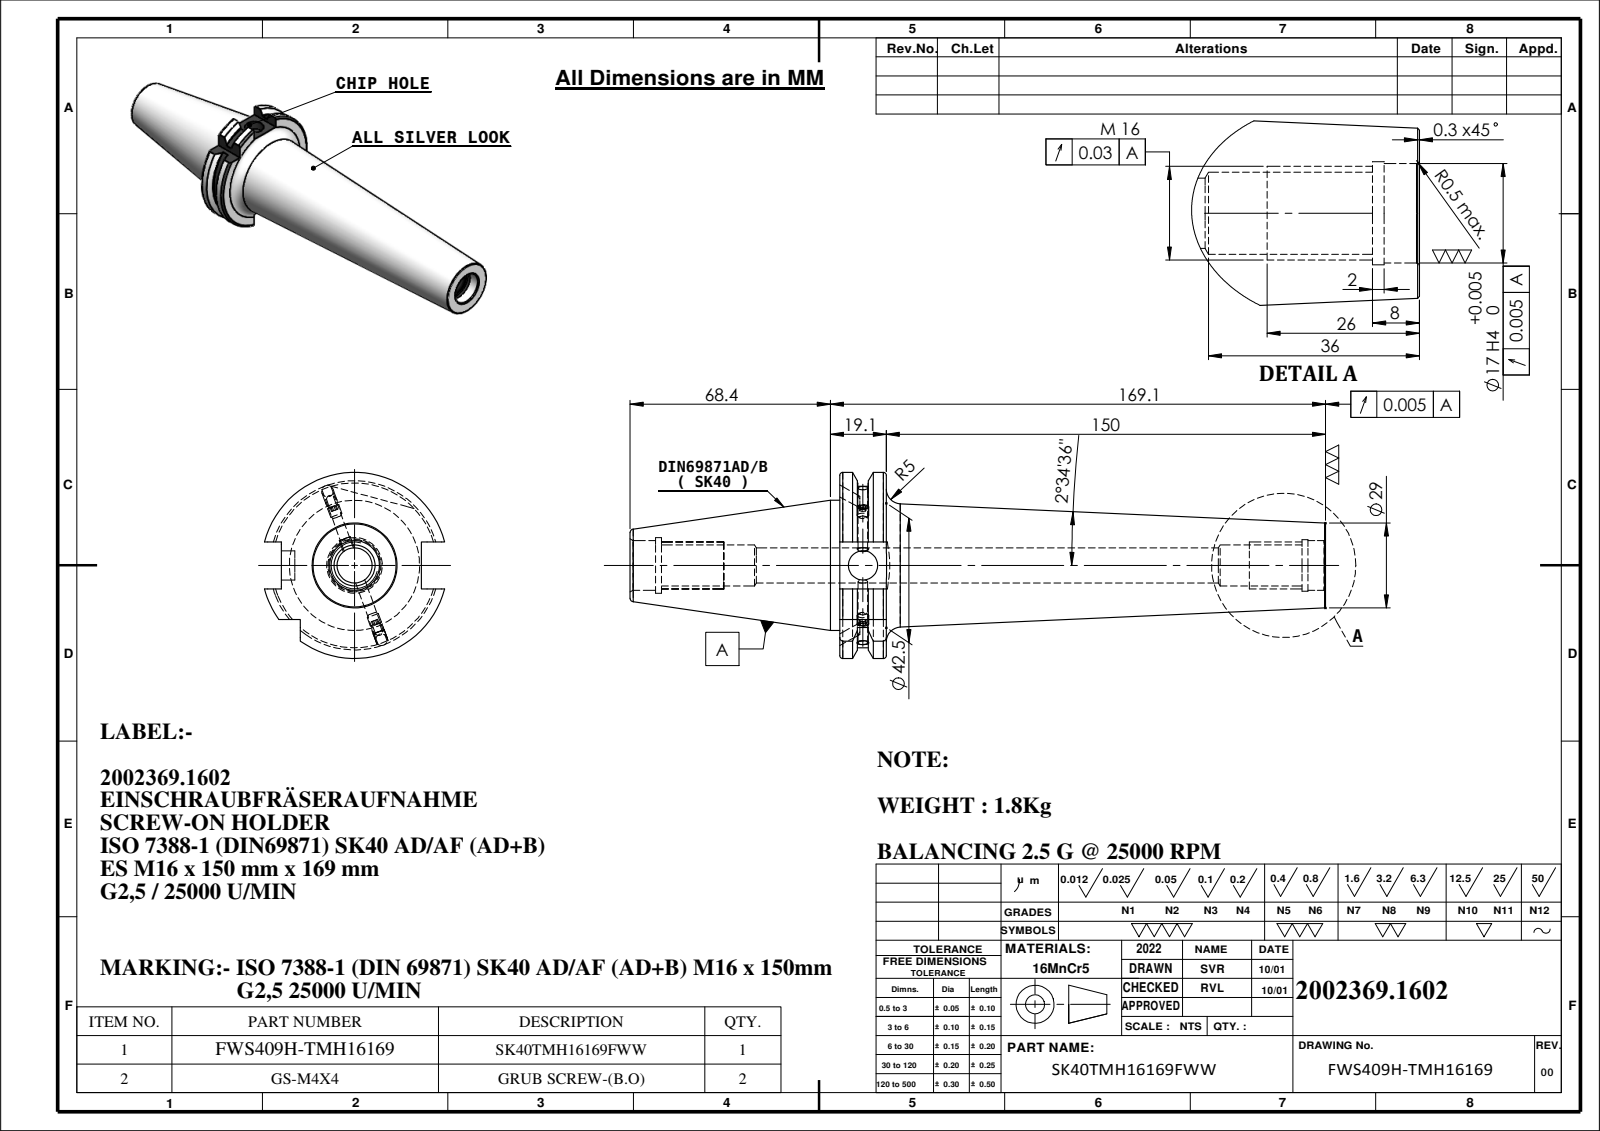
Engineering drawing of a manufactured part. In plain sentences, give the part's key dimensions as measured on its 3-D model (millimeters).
The part is named "Copy of M4X4; SK40TMH16169FWW; Copy of M4X4_DIN 913 - M4 x 4-N; 91406-ES7M16150". Its 3-D file was written by "SolidWorks 2018 (CONFIG_CONTROL_DESIGN)". It is 3 solids with 133 faces: 49 planar, 38 cylindrical and 46 other. Overall it measures 237.5 by 63.55 by 61.48 millimeters. Its volume is 234 142 cubic millimeters and its surface area 43 042 square millimeters. Round holes: 1 of diameter 3.3, 1 of diameter 10, 1 of diameter 12, 1 of diameter 14, 1 of diameter 17, 1 of diameter 17.6, 1 of diameter 19. Round bosses or shafts: 2 of diameter 4, 1 of diameter 44.45. Partial cylindrical surfaces (rounded edges, fillets, slot ends): 1 of radius 28.12, 1 of radius 31.77. The main face-to-face distances are 15.9, 165.9, 150, 16.1, 47.8, 71.6, 87.5, 237.5, 10.7, 60.9.
